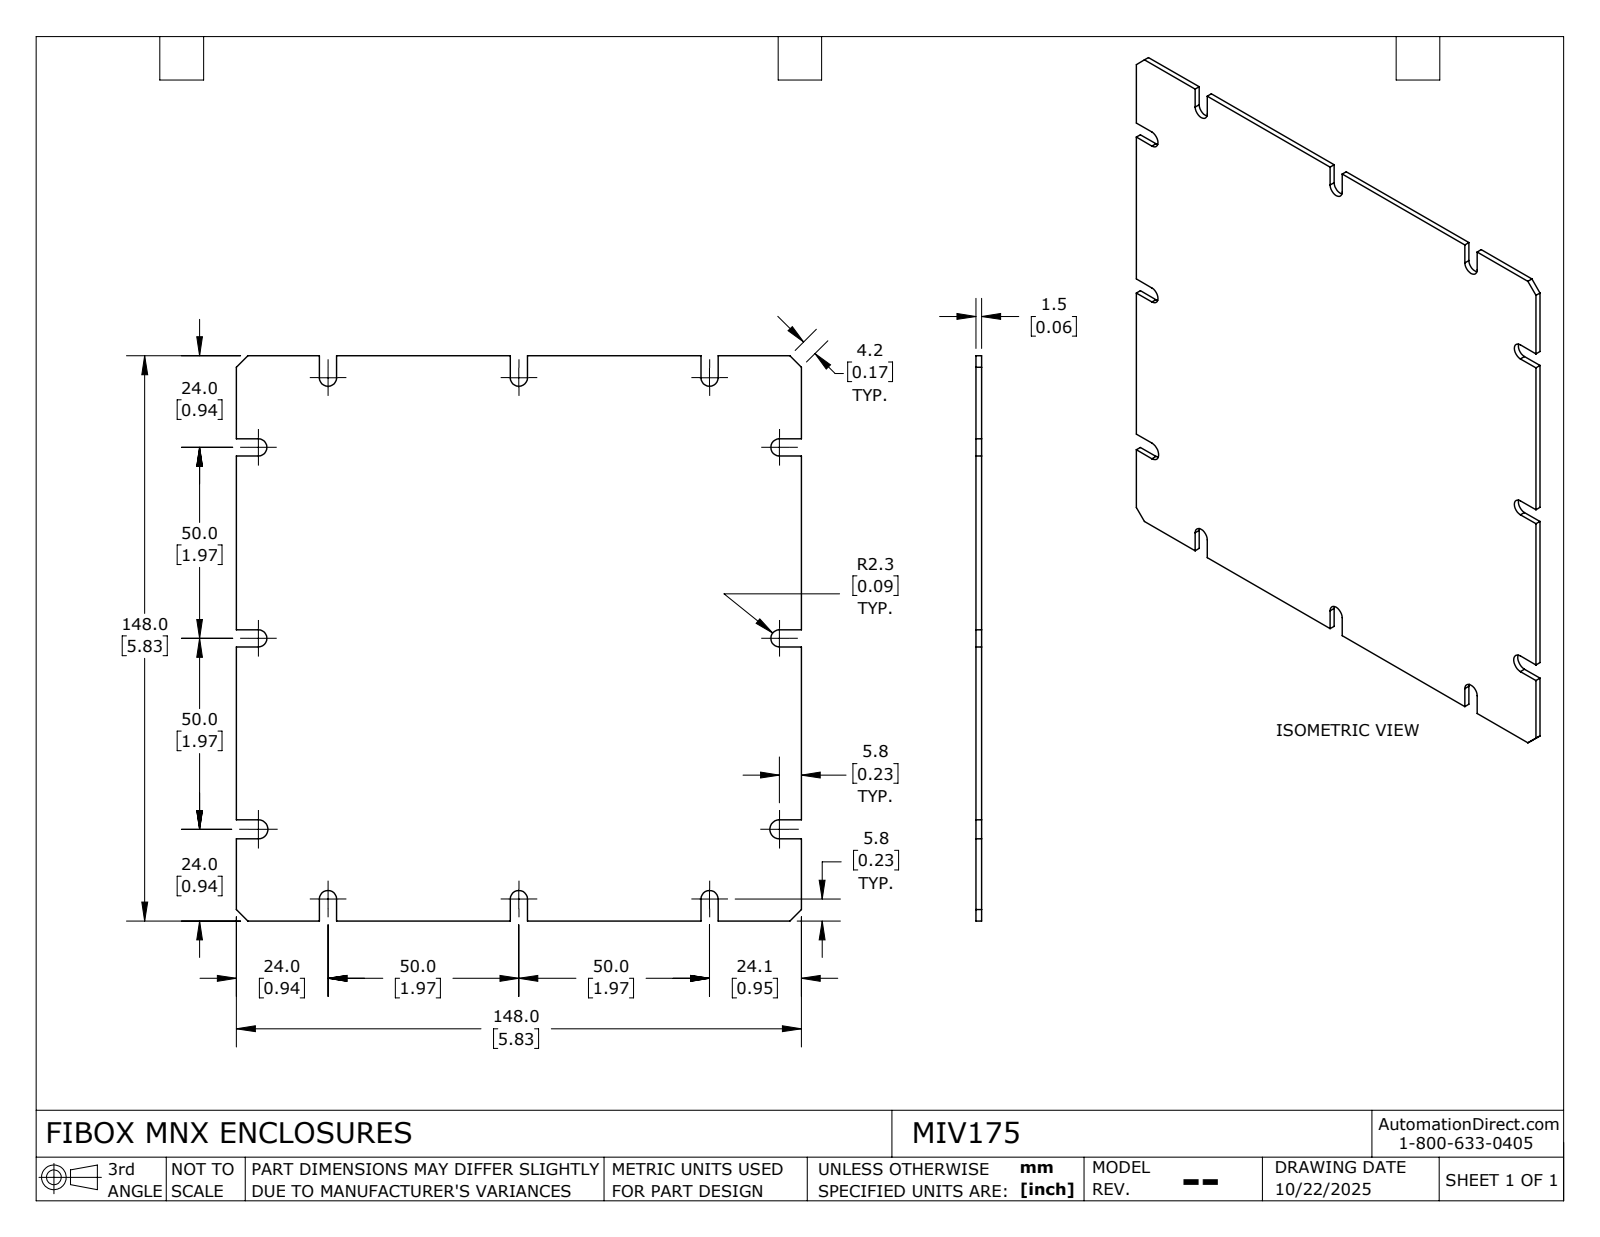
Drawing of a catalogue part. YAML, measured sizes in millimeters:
part_name: "MIV175_Default"
step_written_by: "SolidWorks 2024 (CONFIG_CONTROL_DESIGN)"
units: millimeters
bodies: {solids: 1, faces: 58, planar: 46, cylindrical: 12, other: 0}
overall_size: [148, 148, 1.5]
volume: 32206
surface_area: 44073
partial_cylinders:
  - {radius: 2.25, count: 10}
  - {radius: 2.5, count: 2}
face_to_face_distances: [1.5, 148, 4.5, 71.75, 76.25, 50, 121.75, 126.25, 54.5, 45.5]
